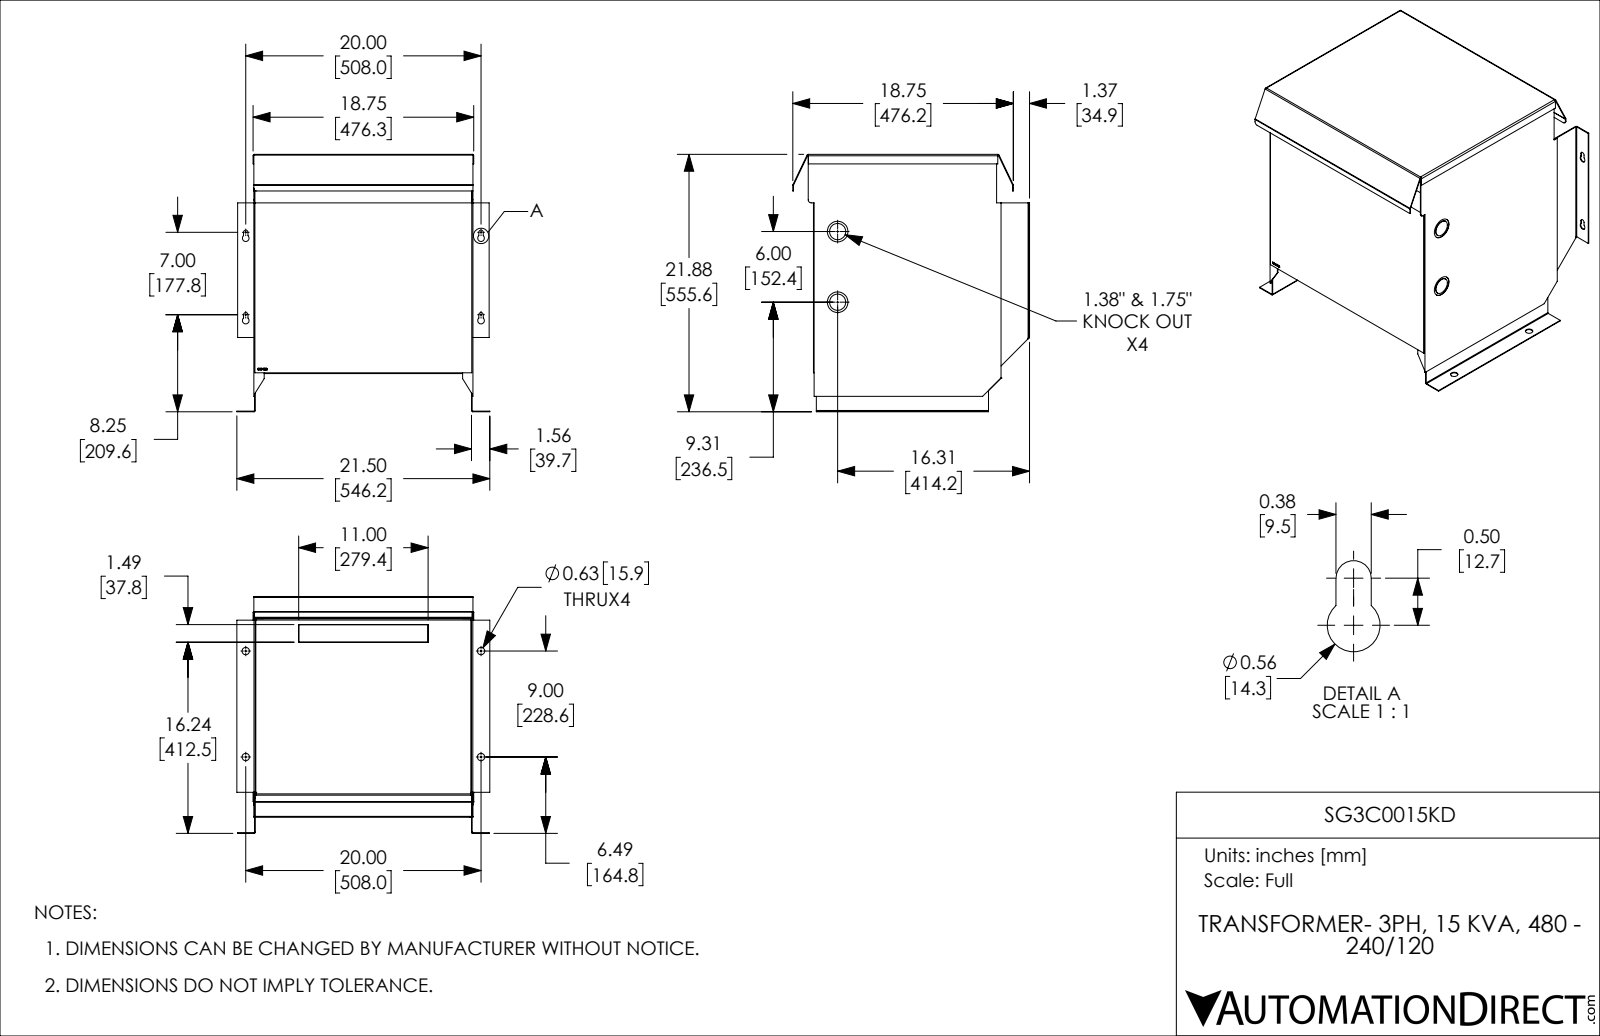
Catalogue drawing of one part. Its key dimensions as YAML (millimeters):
part_name: "SG3C0015KD"
step_written_by: "SolidWorks 2018 (AUTOMOTIVE_DESIGN)"
units: millimeters
bodies: {solids: 7, faces: 313, planar: 205, cylindrical: 80, other: 28}
overall_size: [555.6, 546.2, 511.1]
volume: 2302000
surface_area: 3046000
round_holes:
  - {diameter: 15.9, count: 3}
  - {diameter: 44.5, count: 2}
  - {diameter: 15.9, count: 1}
round_bosses_or_shafts:
  - {diameter: 34.9, count: 2}
partial_cylinders:
  - {radius: 1.3, count: 12}
  - {radius: 2.8, count: 7}
  - {radius: 1.5, count: 6}
  - {radius: 2.9, count: 5}
  - {radius: 3.1, count: 5}
  - {radius: 4.8, count: 4}
  - {radius: 7.1, count: 4}
  - {radius: 6.4, count: 3}
face_to_face_distances: [1.6, 1.5, 471.4, 471.5, 469.9, 1.3, 469.9, 473, 473.1, 382.4]
hole_center_spacings: [228.6, 508, 557.1, 152.4]
